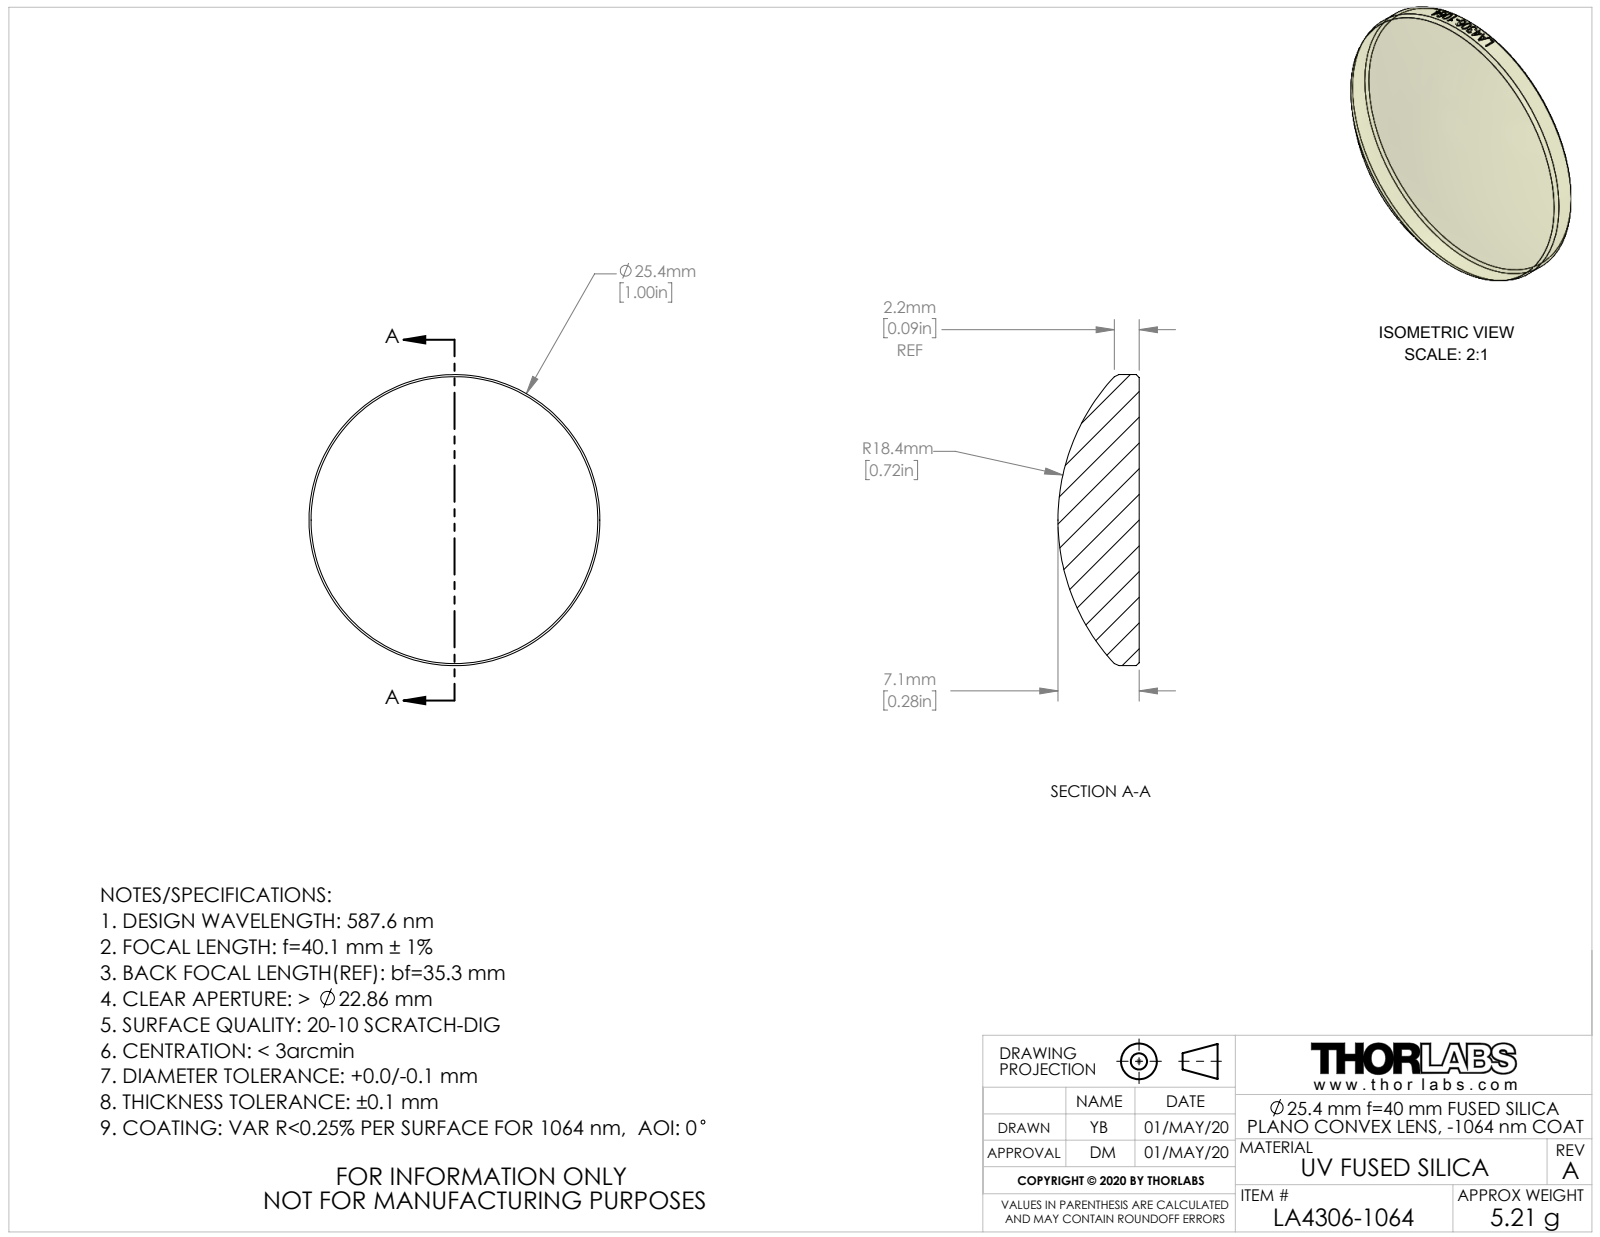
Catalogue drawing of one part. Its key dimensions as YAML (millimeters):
part_name: "CTN015538-E0W"
step_written_by: "SolidWorks 2018 (AUTOMOTIVE_DESIGN)"
units: millimeters
bodies: {solids: 1, faces: 27, planar: 1, cylindrical: 20, other: 6}
overall_size: [25.4, 25.4, 7.08]
volume: 2365
surface_area: 1239
round_bosses_or_shafts:
  - {diameter: 25.4, count: 1}
